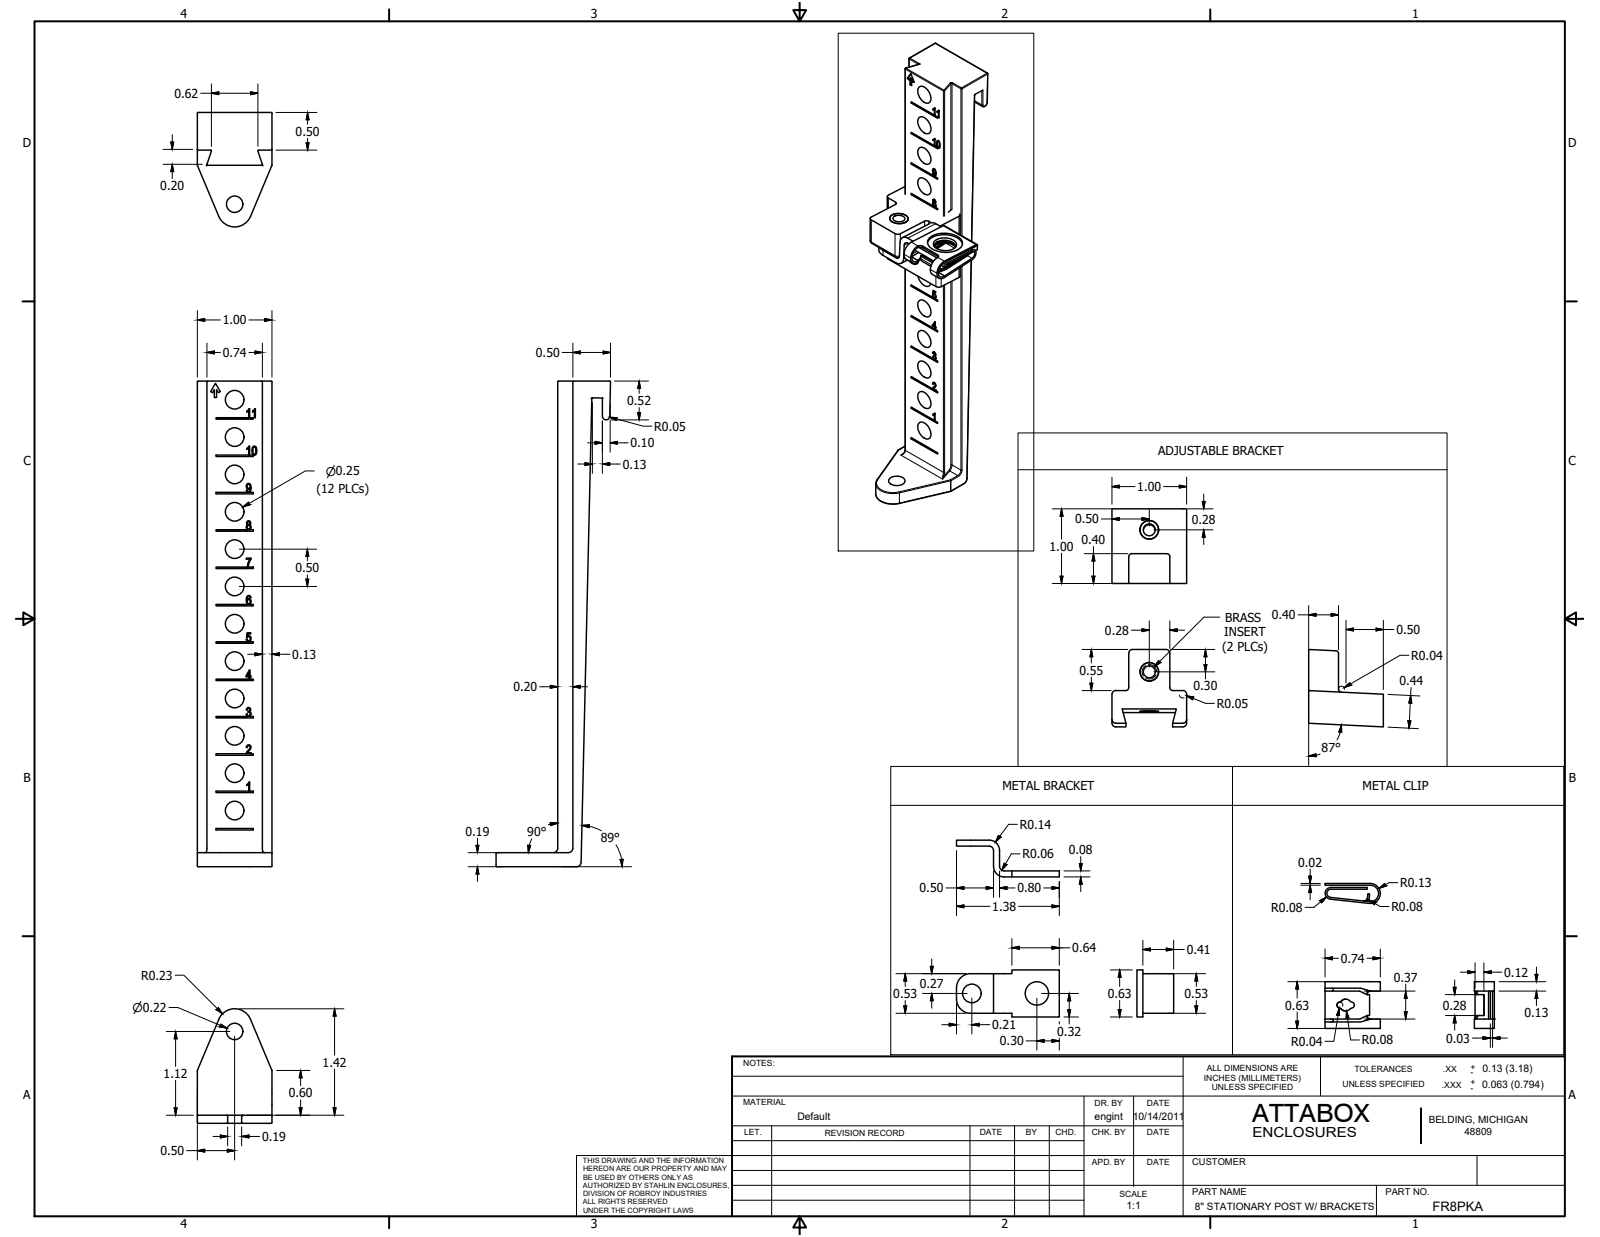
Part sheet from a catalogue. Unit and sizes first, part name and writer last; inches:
Units: inches
Overall size (bounding box): 14.688 × 12.688 × 6.703
Round holes (diameter × count): ⌀0.25 ×48, ⌀0.253 ×8, ⌀0.217 ×4, ⌀0.22 ×4
Round bosses / shafts (diameter × count): ⌀0.19 ×12, ⌀0.373 ×8, ⌀0.433 ×4, ⌀0.315 ×4
Partial cylindrical surfaces — rounded edges, fillets, slot ends (radius × count): R0.01 ×168, R0.06 ×56, R0.049 ×4, R0.23 ×4
Main face-to-face distances: 16.951, 0.203, 17.154, 1, 1.414, 8.472, 8.886, 8.269, 8.683, 7.472
Hole centre spacings: 1.5, 0.5, 1, 1.732, 2.061, 2, 2.45, 2.5
Volume: 10.52 in³ · Surface area: 131.4 in²
Bodies: 24 solids, 1800 faces (916 planar, 332 cylindrical, 552 other)
Part name (STEP PRODUCT): FR8PKA
STEP written by: SolidWorks 2019 (AUTOMOTIVE_DESIGN)
